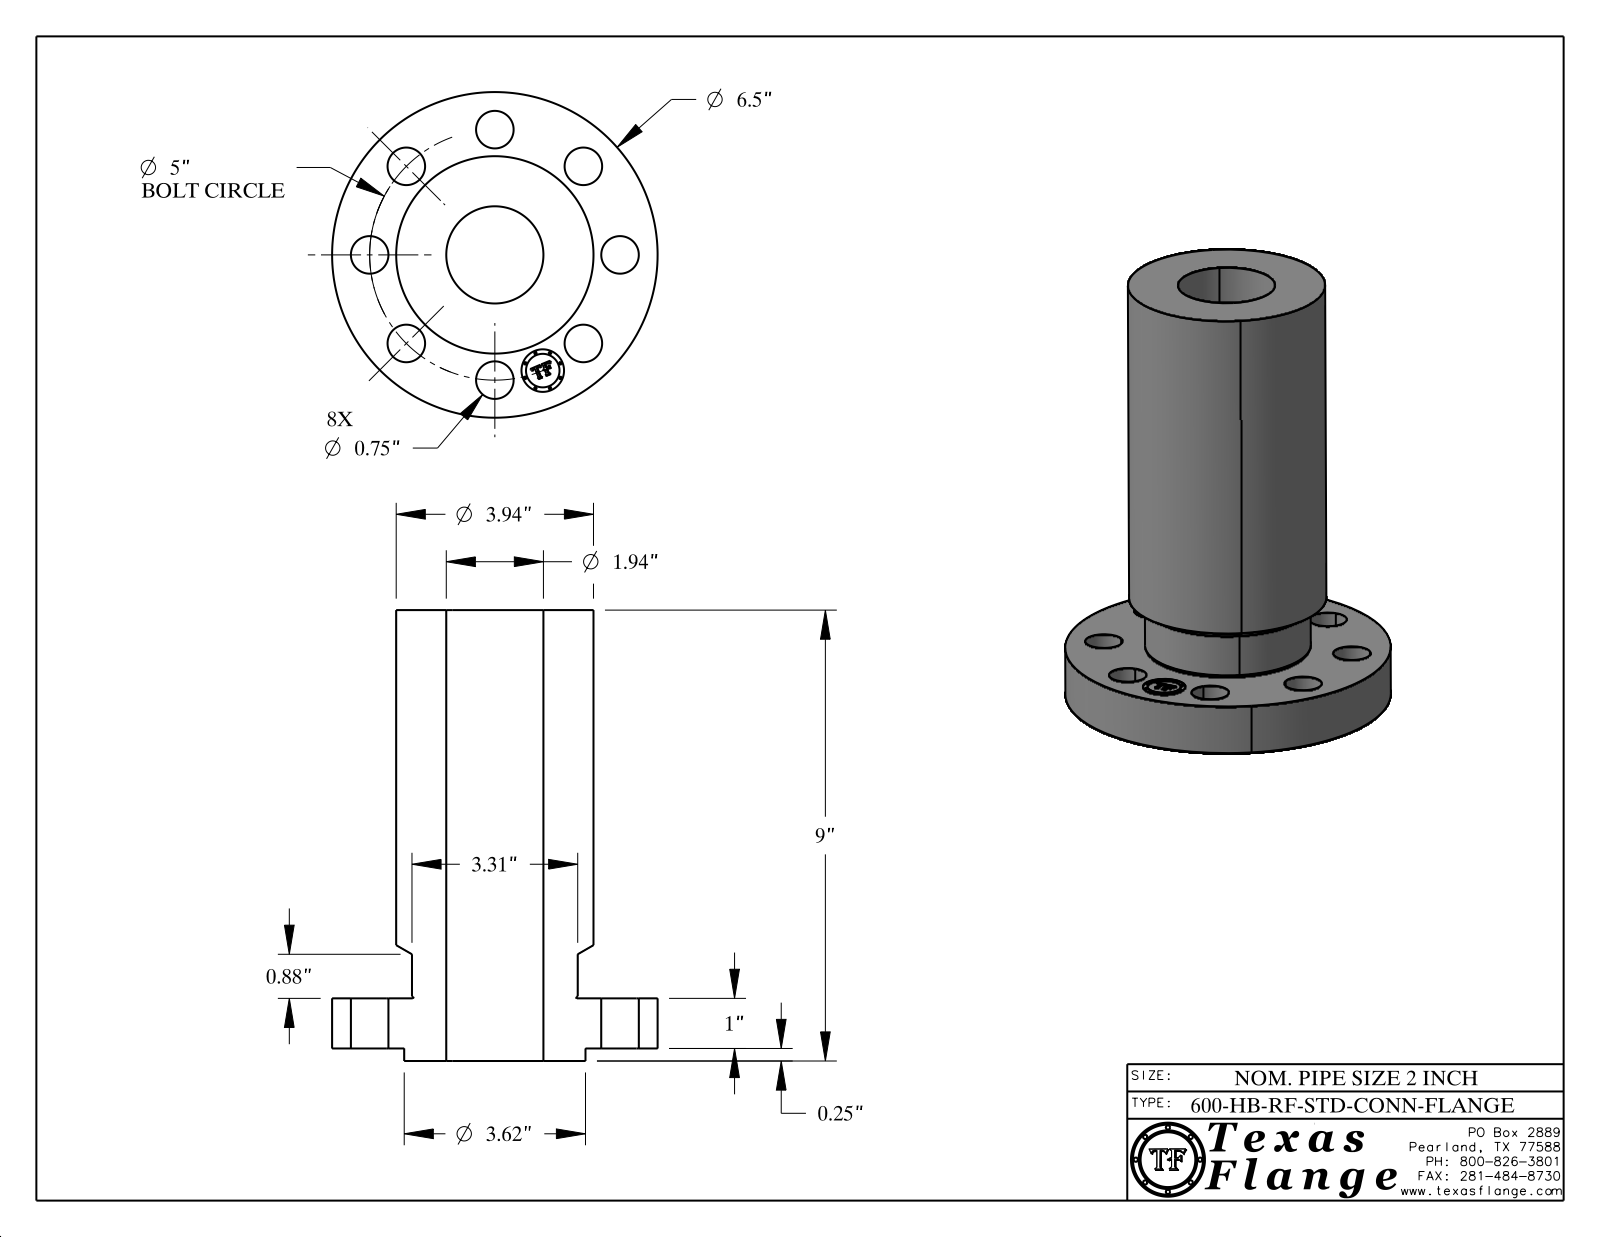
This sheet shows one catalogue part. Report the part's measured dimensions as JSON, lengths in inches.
{"part_name": "2-600-HB-RF-STD-CONN-FLANGE", "step_written_by": "CATIA V5 STEP AP214 (AUTOMOTIVE_DESIGN)", "units": "inches", "bodies": {"solids": 1, "faces": 421, "planar": 369, "cylindrical": 46, "other": 6}, "overall_size": [9, 6.5, 6.5], "volume_in3": 96.61, "surface_area_in2": 250.5, "round_holes": [[0.75, 8], [0.85, 1], [1.94, 1]], "round_bosses_or_shafts": [[0.051, 8], [6.5, 1], [3.94, 1], [3.62, 1], [3.31, 1], [0.67, 1]], "face_to_face_distances": [1, 8.75, 7.75, 0.25, 1.25, 9, 1.245, 0.995, 7.755, 0.254], "hole_center_spacings": [2.5, 1.913, 3.535, 4.619, 5, 0.976, 2.778, 4.157]}
